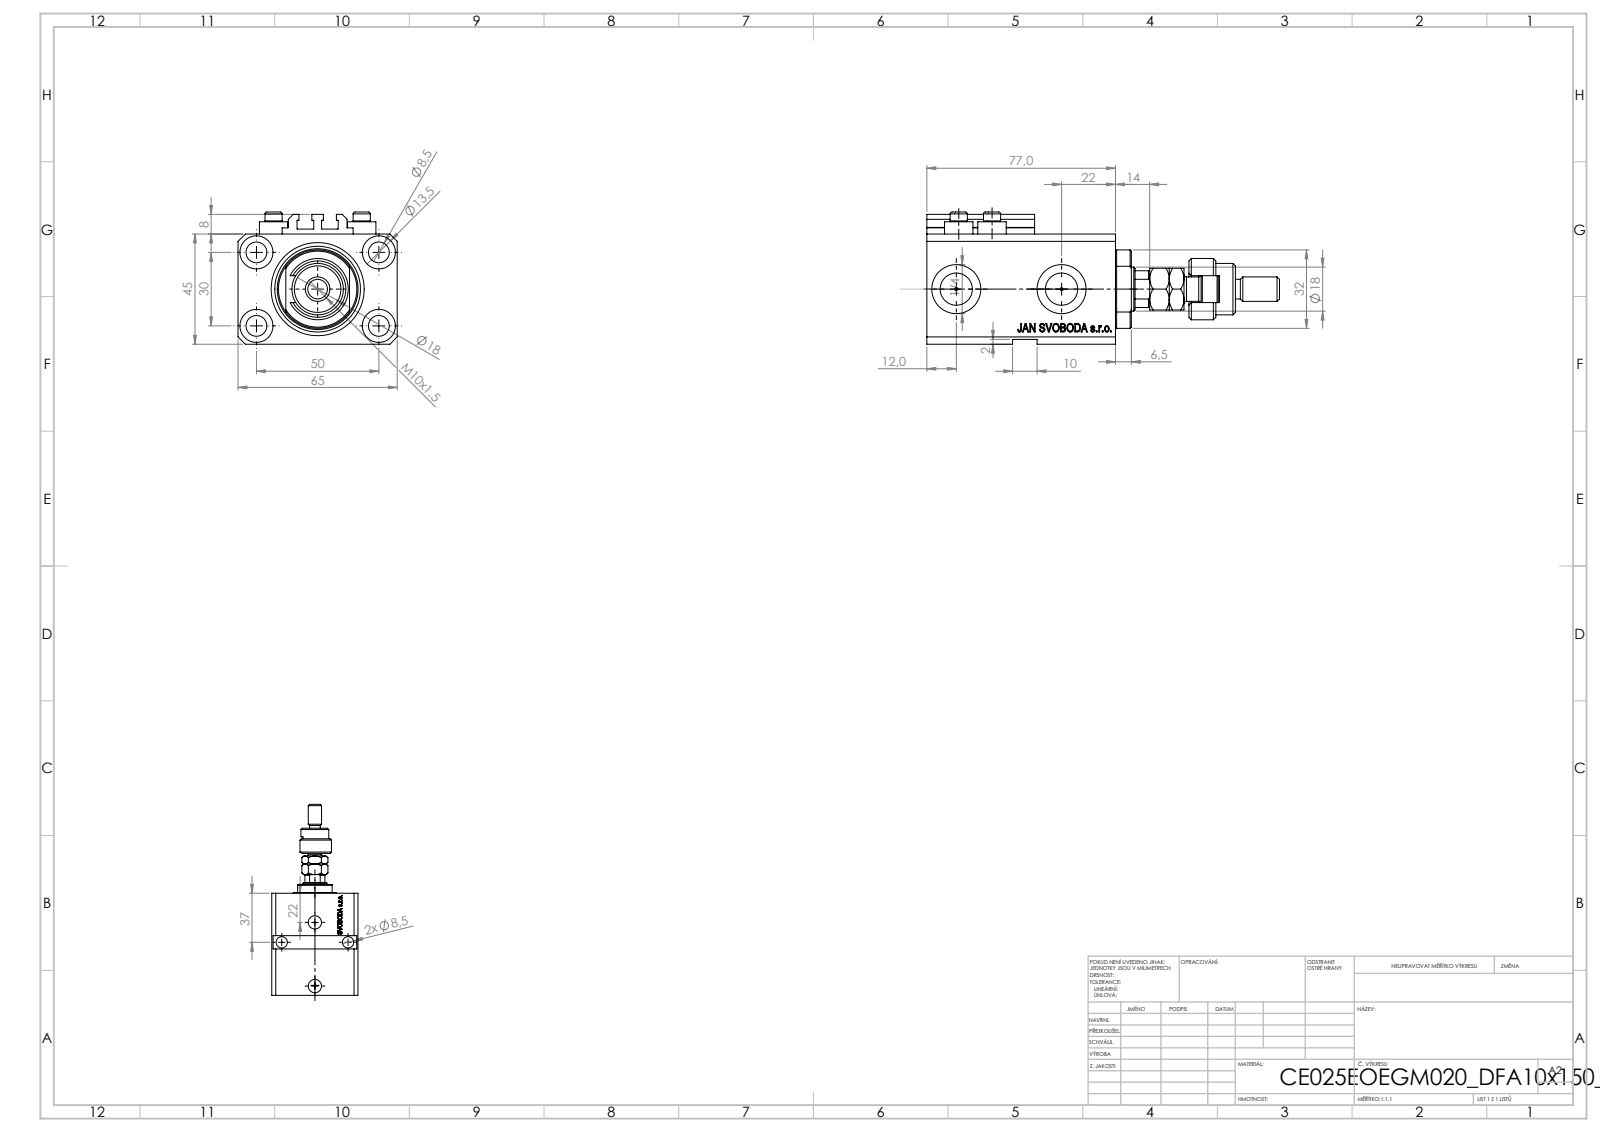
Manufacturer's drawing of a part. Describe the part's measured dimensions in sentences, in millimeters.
The part is named "V250CE_VC_E; FEMALE_PART_FOR_DFA; ALLEN BOLT V250CE; V250CE_E_Body (+2 more)". Its 3-D file was written by "SolidWorks 2019 (CONFIG_CONTROL_DESIGN)". It is 10 solids with 1152 faces: 539 planar, 139 cylindrical and 474 other. Overall it measures 144 by 65 by 54 millimeters. Its volume is 211 569 cubic millimeters and its surface area 64 631 square millimeters. Round holes: 7 of diameter 8.5, 4 of diameter 1.25, 4 of diameter 4, 4 of diameter 13.5, 2 of diameter 10, 2 of diameter 13.16, 2 of diameter 20, 1 of diameter 18, 1 of diameter 38. Round bosses or shafts: 4 of diameter 11.6, 4 of diameter 7, 1 of diameter 25, 1 of diameter 21, 1 of diameter 16, 1 of diameter 10, 1 of diameter 8. Partial cylindrical surfaces (rounded edges, fillets, slot ends): 10 of radius 0.2, 1 of radius 5.5, 1 of radius 8.5, 1 of radius 8.75, 1 of radius 16. The main face-to-face distances are 45, 14, 65, 63, 77, 2, 3, 5, 6.9, 56.1. The hole center spacings are 29.15, 50, 13.6, 15.12, 18.81, 18.97, 26.22, 26.61.
